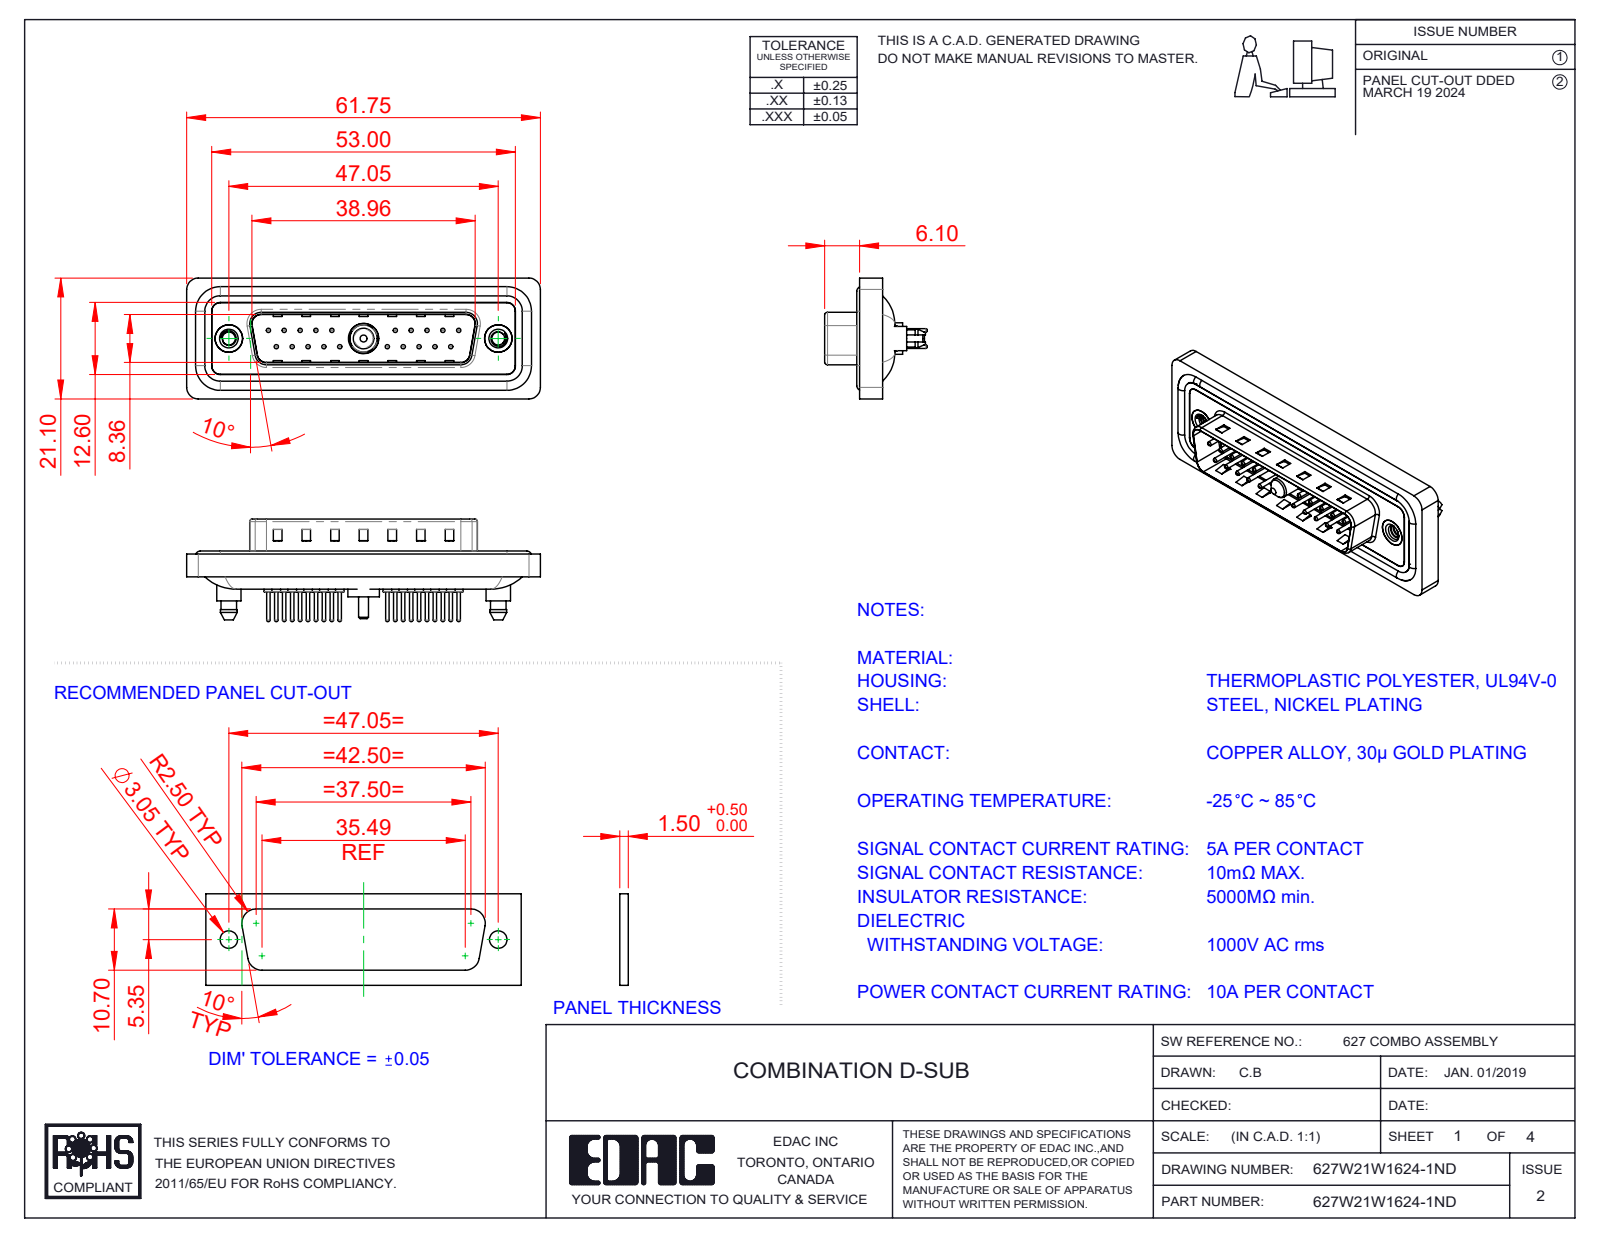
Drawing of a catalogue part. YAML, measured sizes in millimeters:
part_name: "627Combo Housing_21W1; 627Combo Threaded Boardlock_5; 627Combo Threaded Boardlock_D; 627Combo Waterproof Housing_25 Contacts (+6 more)"
step_written_by: "SolidWorks 2023 (CONFIG_CONTROL_DESIGN)"
units: millimeters
bodies: {solids: 29, faces: 1320, planar: 375, cylindrical: 527, other: 418}
overall_size: [61.75, 21.1, 17.9]
volume: 7317
surface_area: 12277
round_holes:
  - {diameter: 0.75, count: 20}
  - {diameter: 1.6, count: 20}
  - {diameter: 2, count: 20}
  - {diameter: 2.26, count: 2}
  - {diameter: 4, count: 2}
  - {diameter: 4.8, count: 2}
  - {diameter: 5, count: 2}
  - {diameter: 4.85, count: 1}
  - {diameter: 5.3, count: 1}
round_bosses_or_shafts:
  - {diameter: 1.5, count: 20}
  - {diameter: 0.6, count: 20}
  - {diameter: 1.6, count: 4}
  - {diameter: 5.4, count: 2}
  - {diameter: 4.9, count: 2}
  - {diameter: 4.25, count: 2}
  - {diameter: 5.5, count: 1}
  - {diameter: 5.2, count: 1}
partial_cylinders:
  - {radius: 1.5, count: 24}
  - {radius: 2, count: 18}
  - {radius: 1.6, count: 10}
  - {radius: 0.5, count: 8}
  - {radius: 0.25, count: 4}
  - {radius: 0.6, count: 4}
  - {radius: 0.65, count: 4}
  - {radius: 0.9, count: 4}
face_to_face_distances: [0.4, 1.5, 1.1, 1.6, 0.5, 3.1, 2.9, 4.1, 0.82, 9.58]
hole_center_spacings: [3.16, 2.77, 5.54, 8.31, 5.04, 19.39, 20.97, 22.16]
